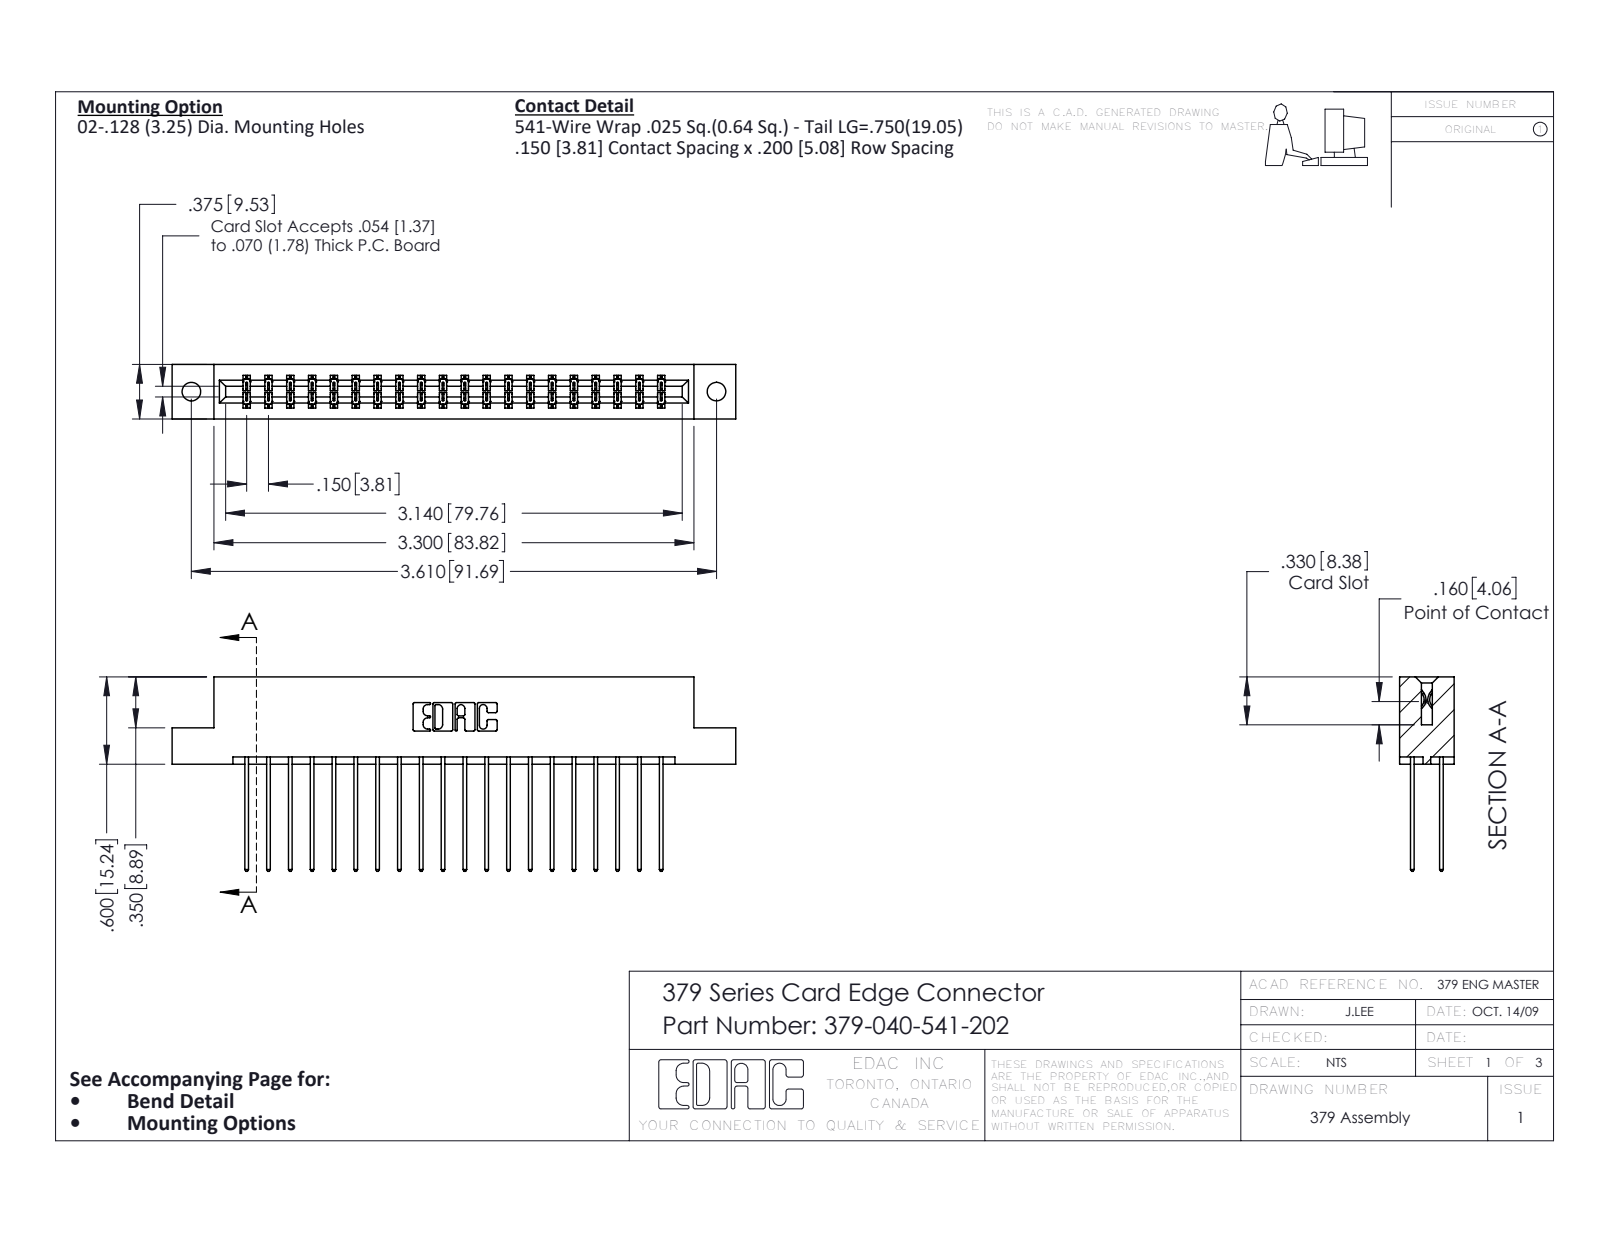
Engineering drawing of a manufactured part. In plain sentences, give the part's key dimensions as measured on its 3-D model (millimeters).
The part is named "345-292-001_345-293-141; 379 Part_Flush - .128 Dia; 379-040-541-202". Its 3-D file was written by "SolidWorks 2016 (CONFIG_CONTROL_DESIGN)". It is 41 solids with 2194 faces: 1510 planar, 684 cylindrical and 0 other. Overall it measures 98.4 by 34 by 9.5 millimeters. Its volume is 10 400 cubic millimeters and its surface area 12 360 square millimeters. Round holes: 2 of diameter 3.3. Partial cylindrical surfaces (rounded edges, fillets, slot ends): 60 of radius 0.2, 40 of radius 0.3, 22 of radius 0.3, 6 of radius 0.2, 6 of radius 0.8, 3 of radius 0.7, 2 of radius 0.4, 2 of radius 0.6. The main face-to-face distances are 7.6, 1.9, 9.5, 7, 2.5, 5.1, 15.2, 0.6, 1.9, 3.8. The hole center spacings are 91.7.
